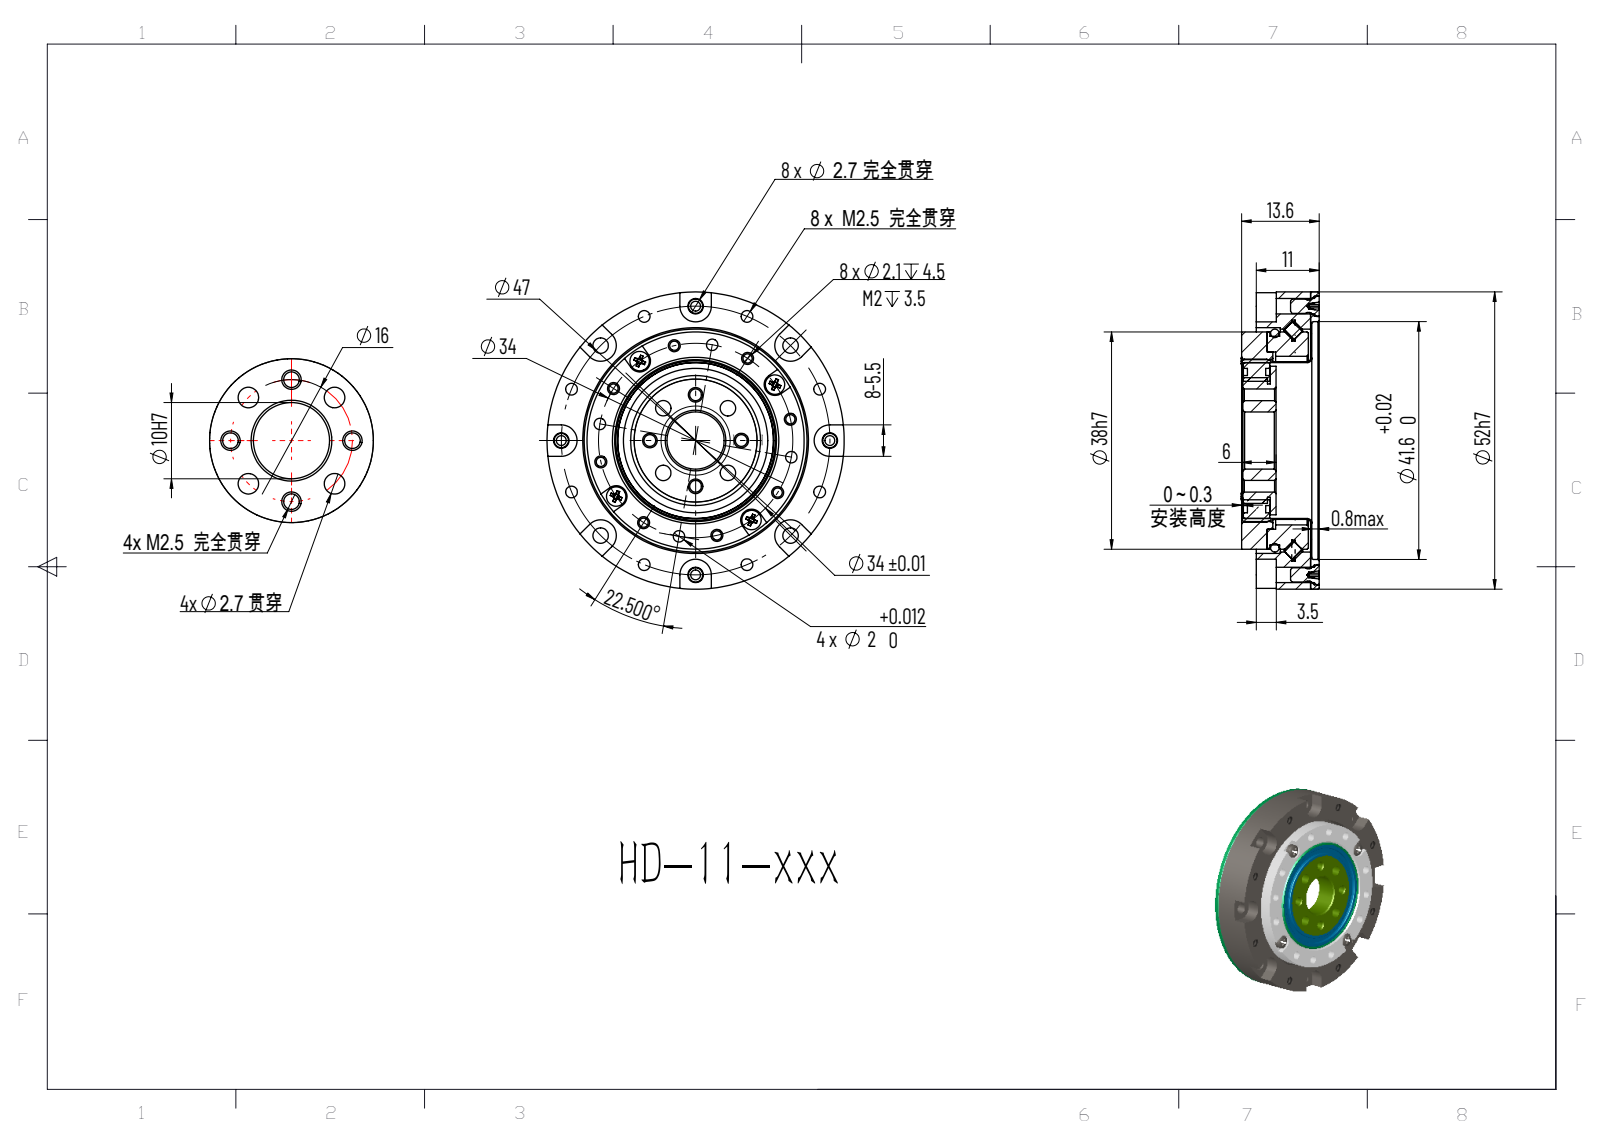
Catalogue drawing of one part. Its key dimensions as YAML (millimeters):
part_name: "HD-11-xxx; HD-11-02??_??; HD-11-01??; HD-11-????_?? <1> (+8 more)"
step_written_by: "ONSHAPE BY PTC INC, 1.201 (AP242_MANAGED_MODEL_BASED_3D_ENGINEERING_MIM_LF)"
units: millimeters
bodies: {solids: 65, faces: 817, planar: 416, cylindrical: 194, other: 207}
overall_size: [52, 52, 13.62]
volume: 16940
surface_area: 22568
round_holes:
  - {diameter: 2.7, count: 20}
  - {diameter: 1.6, count: 12}
  - {diameter: 2.05, count: 12}
  - {diameter: 2, count: 8}
  - {diameter: 2.1, count: 8}
  - {diameter: 3.6, count: 4}
  - {diameter: 1.25, count: 1}
  - {diameter: 1.7, count: 1}
  - {diameter: 10, count: 1}
  - {diameter: 20.73, count: 1}
  - {diameter: 25.26, count: 1}
  - {diameter: 27.26, count: 1}
round_bosses_or_shafts:
  - {diameter: 2.5, count: 52}
  - {diameter: 3.5, count: 4}
  - {diameter: 3.4, count: 4}
  - {diameter: 2.17, count: 4}
  - {diameter: 1.73, count: 4}
  - {diameter: 52, count: 1}
  - {diameter: 38, count: 1}
  - {diameter: 36.5, count: 1}
partial_cylinders:
  - {radius: 2.75, count: 8}
  - {radius: 1.9, count: 4}
  - {radius: 1.5, count: 1}
face_to_face_distances: [1.9, 9.1, 1.5, 9.5, 9.73, 7.83, 7.6, 1.27, 11, 1.55]
hole_center_spacings: [39.08, 46.1, 7.35, 31.27, 9.17, 17.99, 20.34, 26.11]
